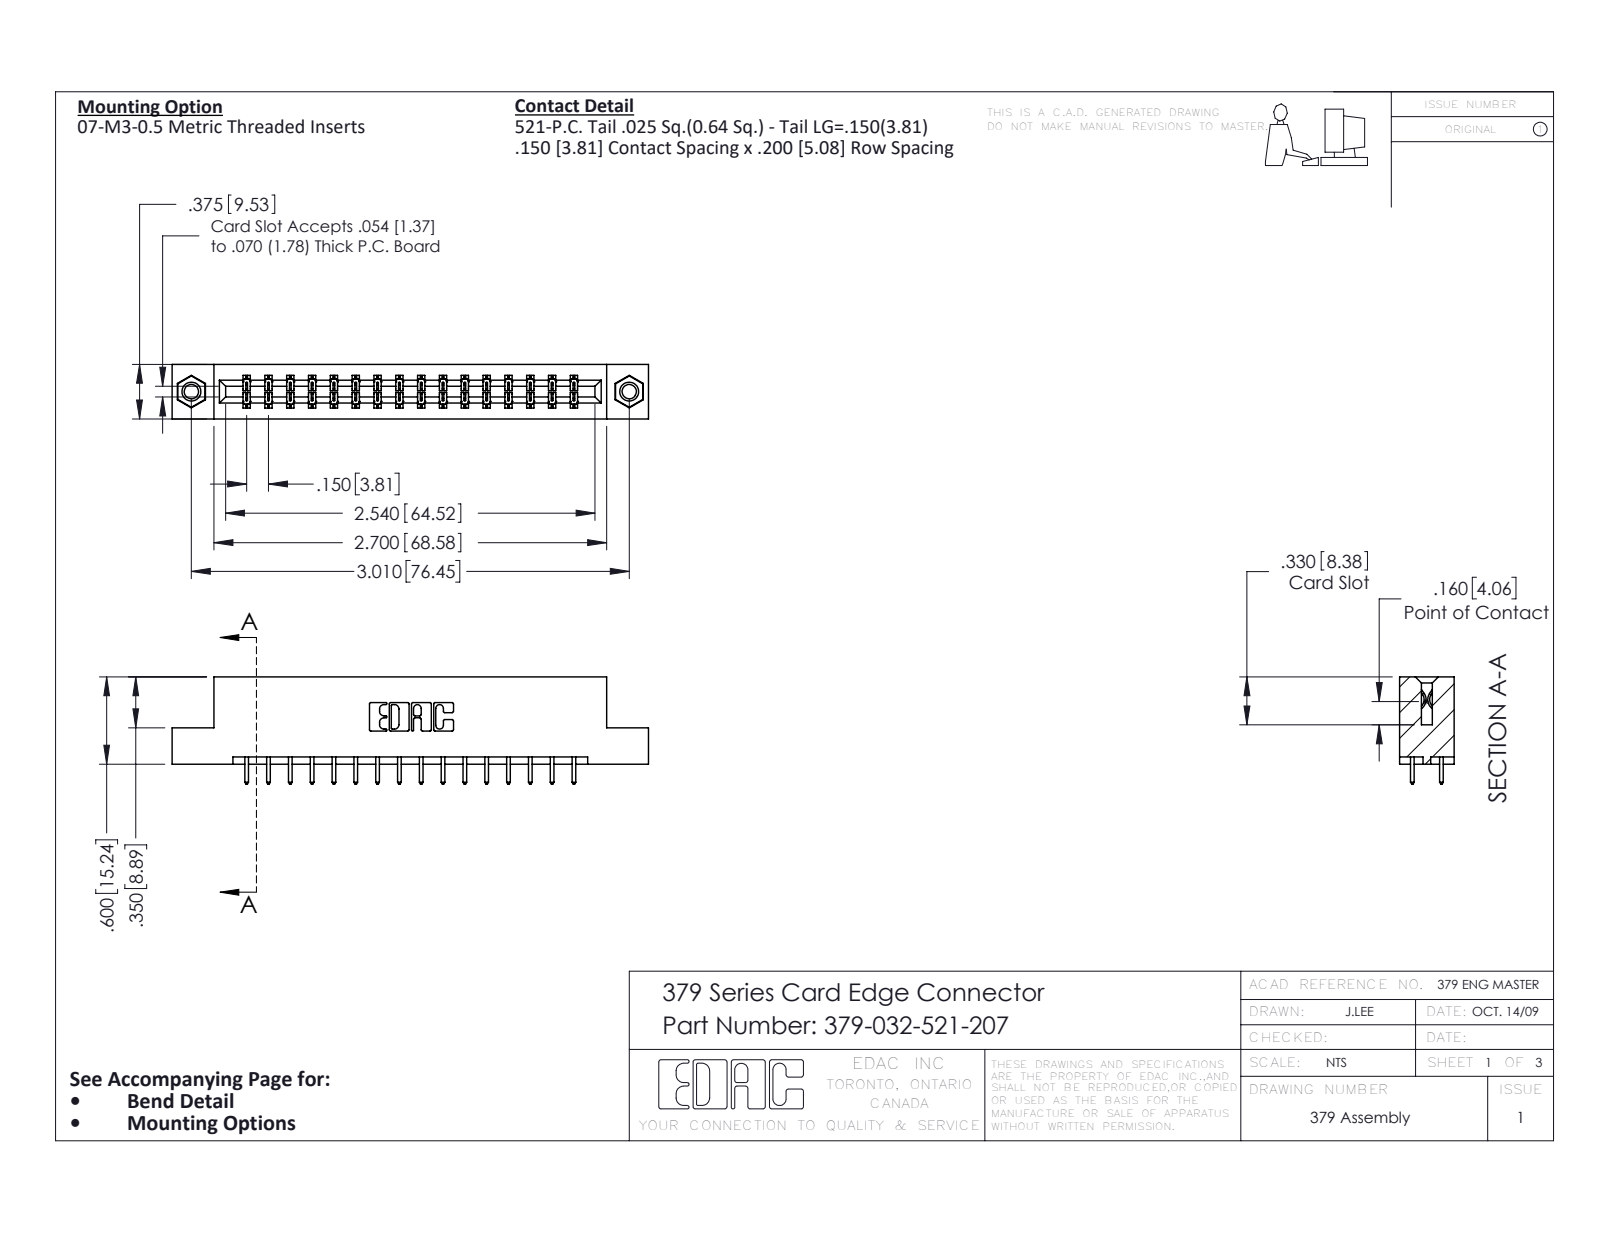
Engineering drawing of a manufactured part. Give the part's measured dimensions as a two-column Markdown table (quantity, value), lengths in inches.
| quantity | value |
| --- | --- |
| part name | 345-250-001_345-250-005-103; 379 Part_Flush - .156 Dia - TI; 379-032-521-207; 345-292-001_345-293-121 |
| STEP written by | SolidWorks 2020 (CONFIG_CONTROL_DESIGN) |
| units | inches |
| bodies | 35 solids, 1838 faces (1254 planar, 568 cylindrical, 16 other) |
| overall size | 3.275 × 0.737 × 0.375 |
| volume | 0.519 in³ |
| surface area | 14.35 in² |
| round holes (diameter × count) | 0.098 × 2, 0.125 × 2, 0.156 × 2 |
| round bosses / shafts (diameter × count) | 0.155 × 2 |
| partial cylindrical surfaces (radius × count) | 0.006 × 63, 0.01 × 32, 0.01 × 22, 0.007 × 6, 0.031 × 6, 0.026 × 3, 0.014 × 2, 0.022 × 2 |
| main face-to-face distances | 0.3, 0.075, 0.375, 0.2, 0.1, 0.15, 0.05, 0.6, 0.225, 0.55 |
| hole center spacings | 3.01 |
